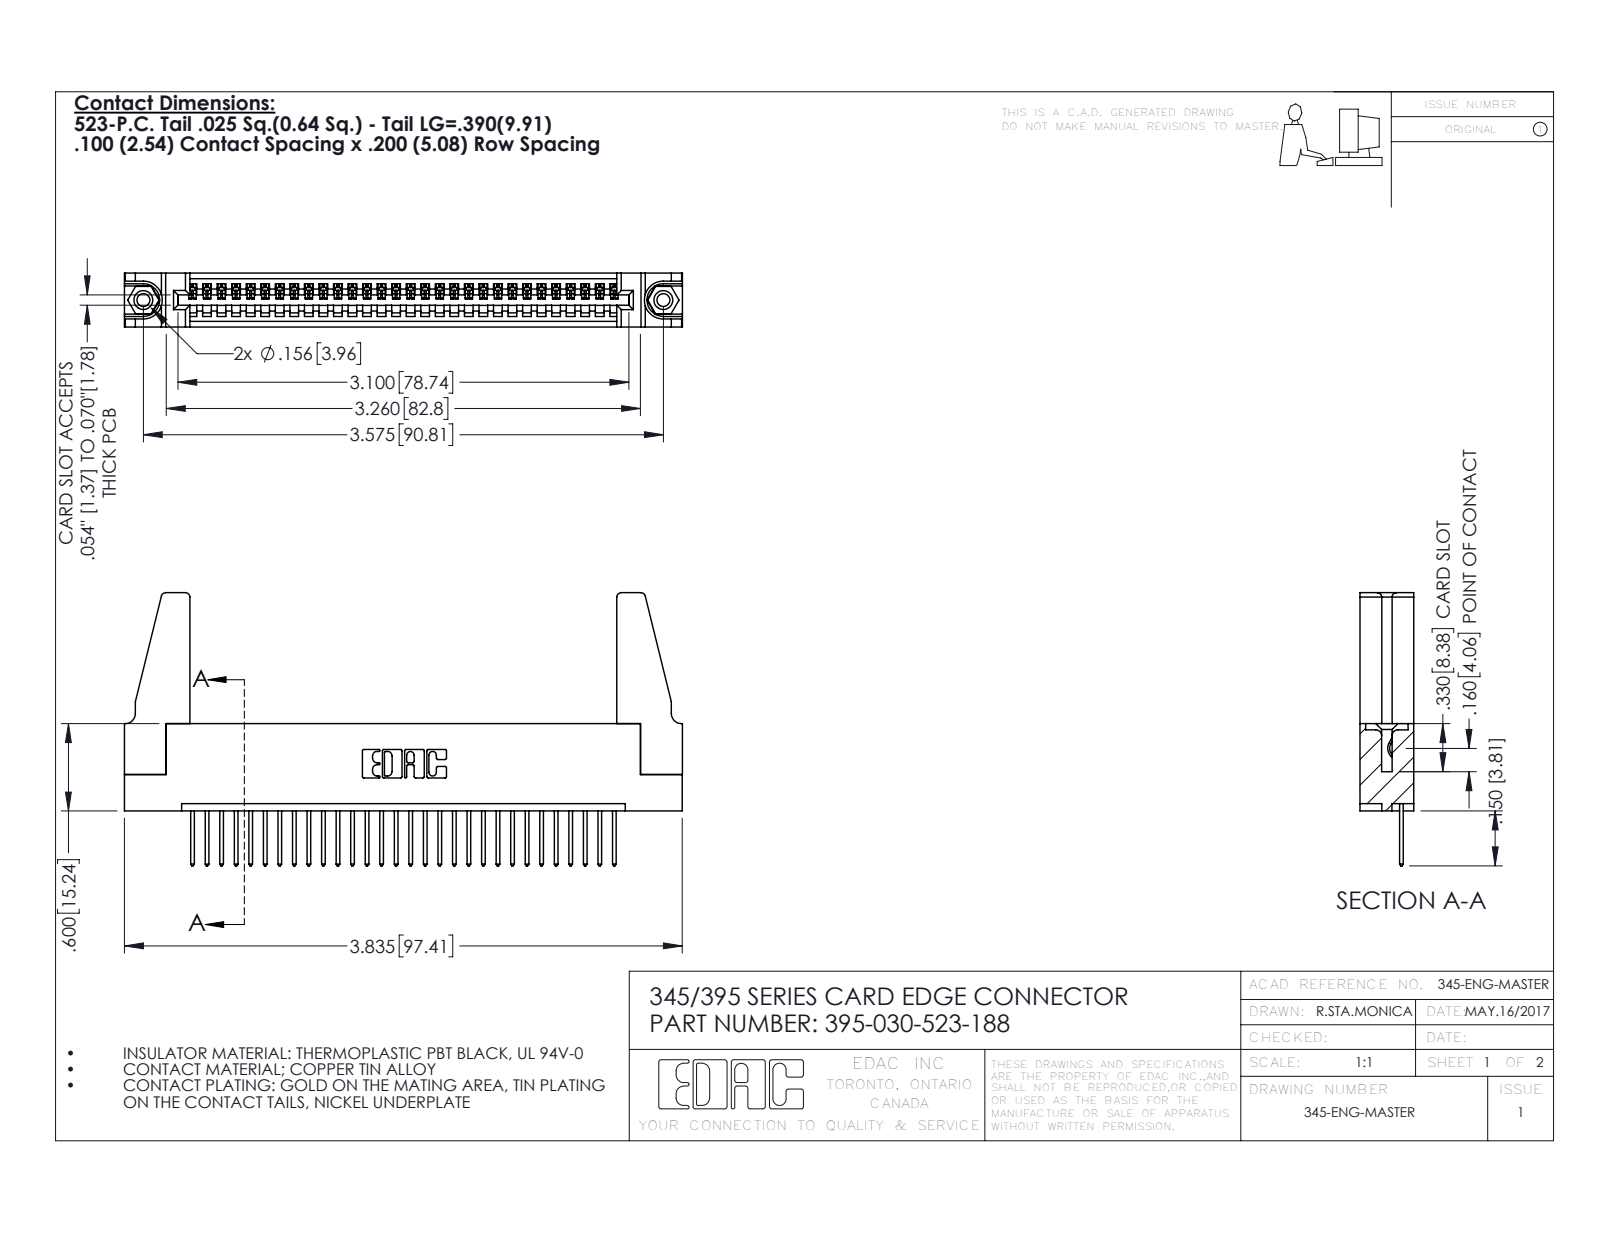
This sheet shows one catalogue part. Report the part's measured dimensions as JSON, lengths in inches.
{"part_name": "345-250-001_345-250-001-102; 345-220-078_345-220-088; 345 Part_Flush Mounting Lugs - 0.156 Dia-TH; 345-292-001_345-293-123 (+1 more)", "step_written_by": "SolidWorks 2016 (CONFIG_CONTROL_DESIGN)", "units": "inches", "bodies": {"solids": 35, "faces": 1990, "planar": 1352, "cylindrical": 622, "other": 16}, "overall_size": [3.836, 1.877, 0.37], "volume_in3": 0.757, "surface_area_in2": 23.48, "round_holes": [[0.089, 2], [0.125, 2], [0.156, 2], [0.064, 1]], "round_bosses_or_shafts": [[0.155, 2]], "partial_cylinders_radius": [[0.006, 60], [0.01, 60], [0.01, 22], [0.03, 8], [0.007, 6], [0.031, 6], [0.026, 3], [0.031, 2]], "face_to_face_distances": [0.072, 0.298, 0.37, 0.2, 0.098, 0.272, 0.025, 0.225, 0.149, 0.072], "hole_center_spacings": [0.27, 3.34, 3.575]}
